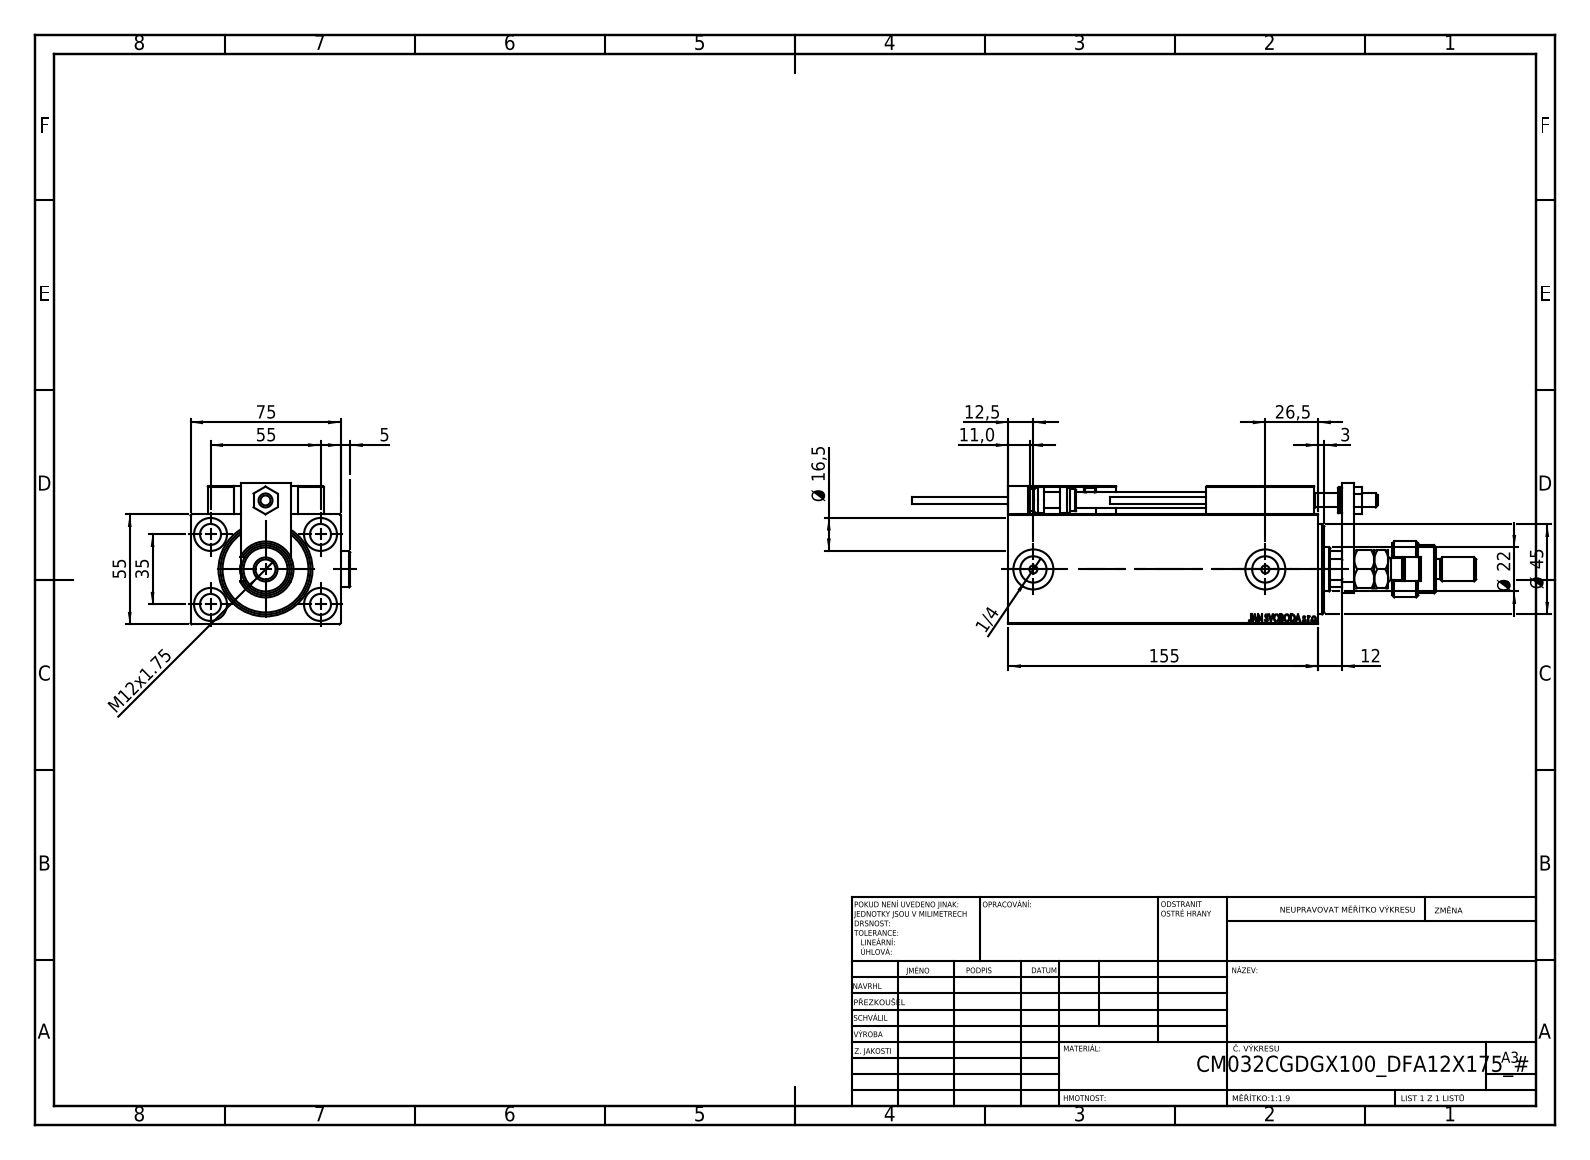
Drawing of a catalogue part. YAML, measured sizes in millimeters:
part_name: "NUT_D12; ZARAZKA; ALLEN BOLT D8; SWITCH DIM B,W (+7 more)"
step_written_by: "SolidWorks 2019 (CONFIG_CONTROL_DESIGN)"
units: millimeters
bodies: {solids: 27, faces: 1421, planar: 622, cylindrical: 217, other: 582}
overall_size: [282, 79.9, 70.5]
volume: 601919
surface_area: 141386
round_holes:
  - {diameter: 4, count: 6}
  - {diameter: 8, count: 5}
  - {diameter: 10.5, count: 5}
  - {diameter: 16.5, count: 5}
  - {diameter: 3.2, count: 4}
  - {diameter: 5, count: 2}
  - {diameter: 13.16, count: 2}
  - {diameter: 20, count: 2}
  - {diameter: 7, count: 1}
  - {diameter: 22, count: 1}
  - {diameter: 25.5, count: 1}
  - {diameter: 32, count: 1}
round_bosses_or_shafts:
  - {diameter: 18, count: 3}
  - {diameter: 11, count: 2}
  - {diameter: 5, count: 2}
  - {diameter: 3.8, count: 2}
  - {diameter: 28, count: 1}
  - {diameter: 24, count: 1}
  - {diameter: 13, count: 1}
  - {diameter: 12, count: 1}
partial_cylinders:
  - {radius: 0.3, count: 30}
  - {radius: 3, count: 2}
  - {radius: 9.75, count: 1}
  - {radius: 10.5, count: 1}
face_to_face_distances: [55, 75, 14, 12, 10, 18, 25, 5, 6, 7]
hole_center_spacings: [32.6, 11.37, 20, 29.59, 29.69, 32.33, 35, 36.06]
